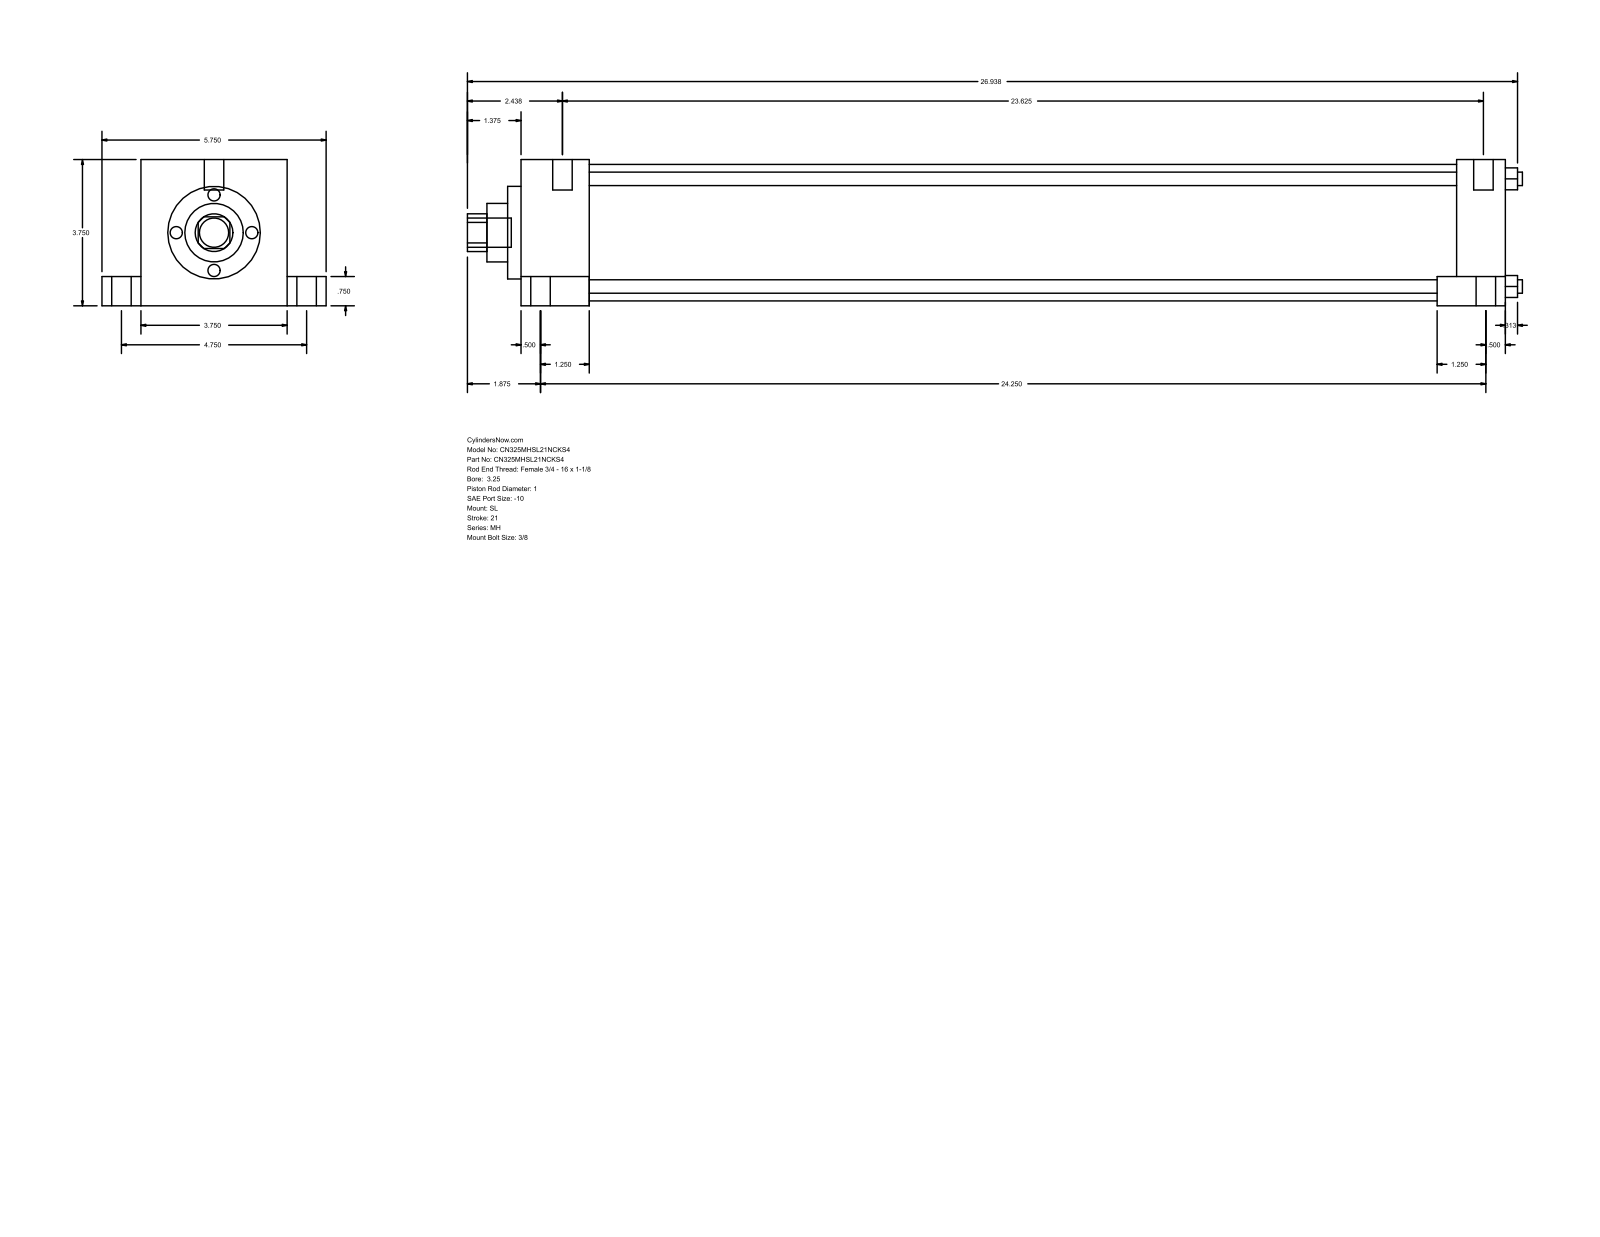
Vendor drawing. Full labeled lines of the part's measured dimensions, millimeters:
Part name (STEP PRODUCT): MH_SL__0325_1
STEP written by: GSSL Pune (CONFIG_CONTROL_DESIGN)
Units: millimetres
Bodies: 0 solids, 110 faces (77 planar, 33 cylindrical, 0 other)
Overall size (bounding box): 687.39 × 146.05 × 95.25
Round holes (diameter × count): ⌀8.76 ×4, ⌀25.4 ×1, ⌀38.1 ×1, ⌀60.33 ×1, ⌀88.9 ×1
Round bosses / shafts (diameter × count): ⌀12.7 ×6, ⌀19.05 ×5, ⌀5.56 ×4
Partial cylindrical surfaces — rounded edges, fillets, slot ends (radius × count): R12.29 ×1
Main face-to-face distances: 95.24, 641.35, 44.46, 596.89, 25.41, 120.65, 19.05, 76.19, 609.6, 565.14
Hole centre spacings: 49.57, 70.1, 99.14
